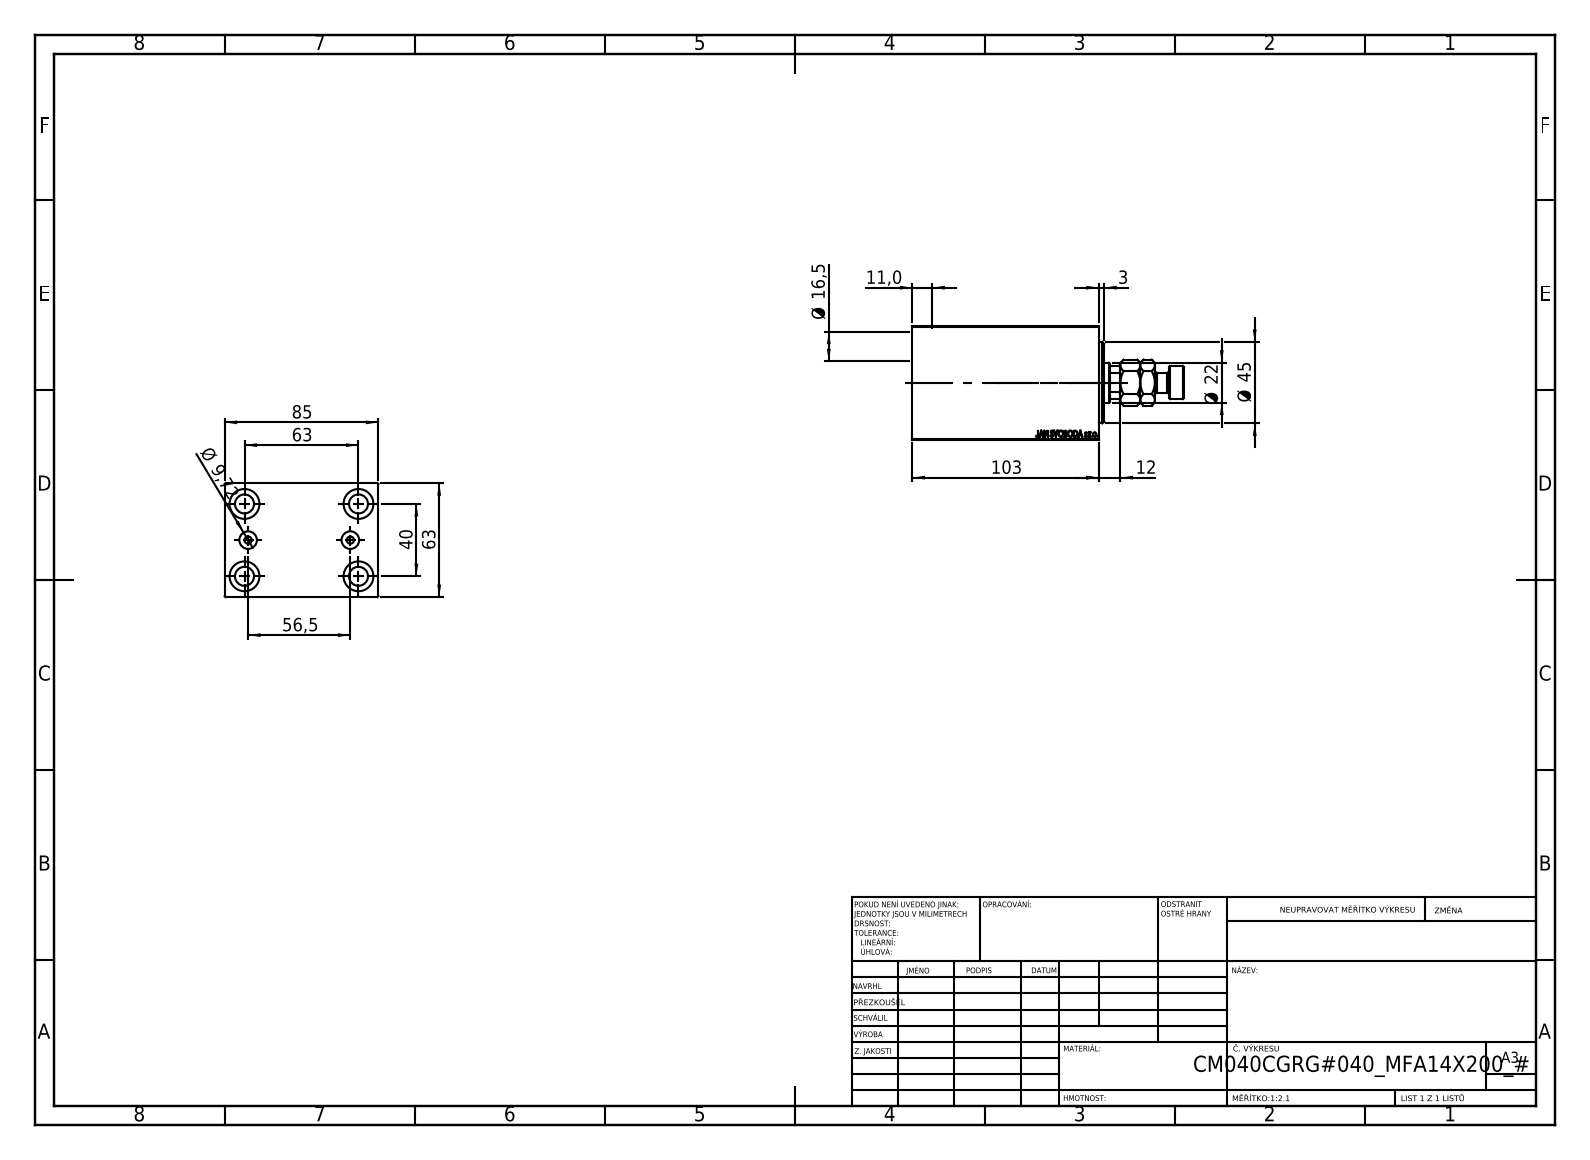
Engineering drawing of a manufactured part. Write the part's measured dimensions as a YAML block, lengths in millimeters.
part_name: "MFA; V450CM_C_Body; V450CM_C_VCP; V450CM_VC_B"
step_written_by: "SolidWorks 2019 (CONFIG_CONTROL_DESIGN)"
units: millimeters
bodies: {solids: 4, faces: 910, planar: 424, cylindrical: 60, other: 426}
overall_size: [150, 85, 63]
volume: 481445
surface_area: 91298
round_holes:
  - {diameter: 10.5, count: 4}
  - {diameter: 16.5, count: 4}
  - {diameter: 4, count: 2}
  - {diameter: 9.72, count: 2}
  - {diameter: 12.5, count: 1}
  - {diameter: 22, count: 1}
  - {diameter: 25.5, count: 1}
  - {diameter: 40, count: 1}
  - {diameter: 42, count: 1}
  - {diameter: 45, count: 1}
round_bosses_or_shafts:
  - {diameter: 18, count: 1}
  - {diameter: 11, count: 1}
partial_cylinders:
  - {radius: 10.5, count: 1}
face_to_face_distances: [63, 85, 12, 91, 103, 40, 1, 79, 52, 11]
hole_center_spacings: [37.31, 20.1, 20.5, 40, 61.82, 63, 64.2, 74.63]
